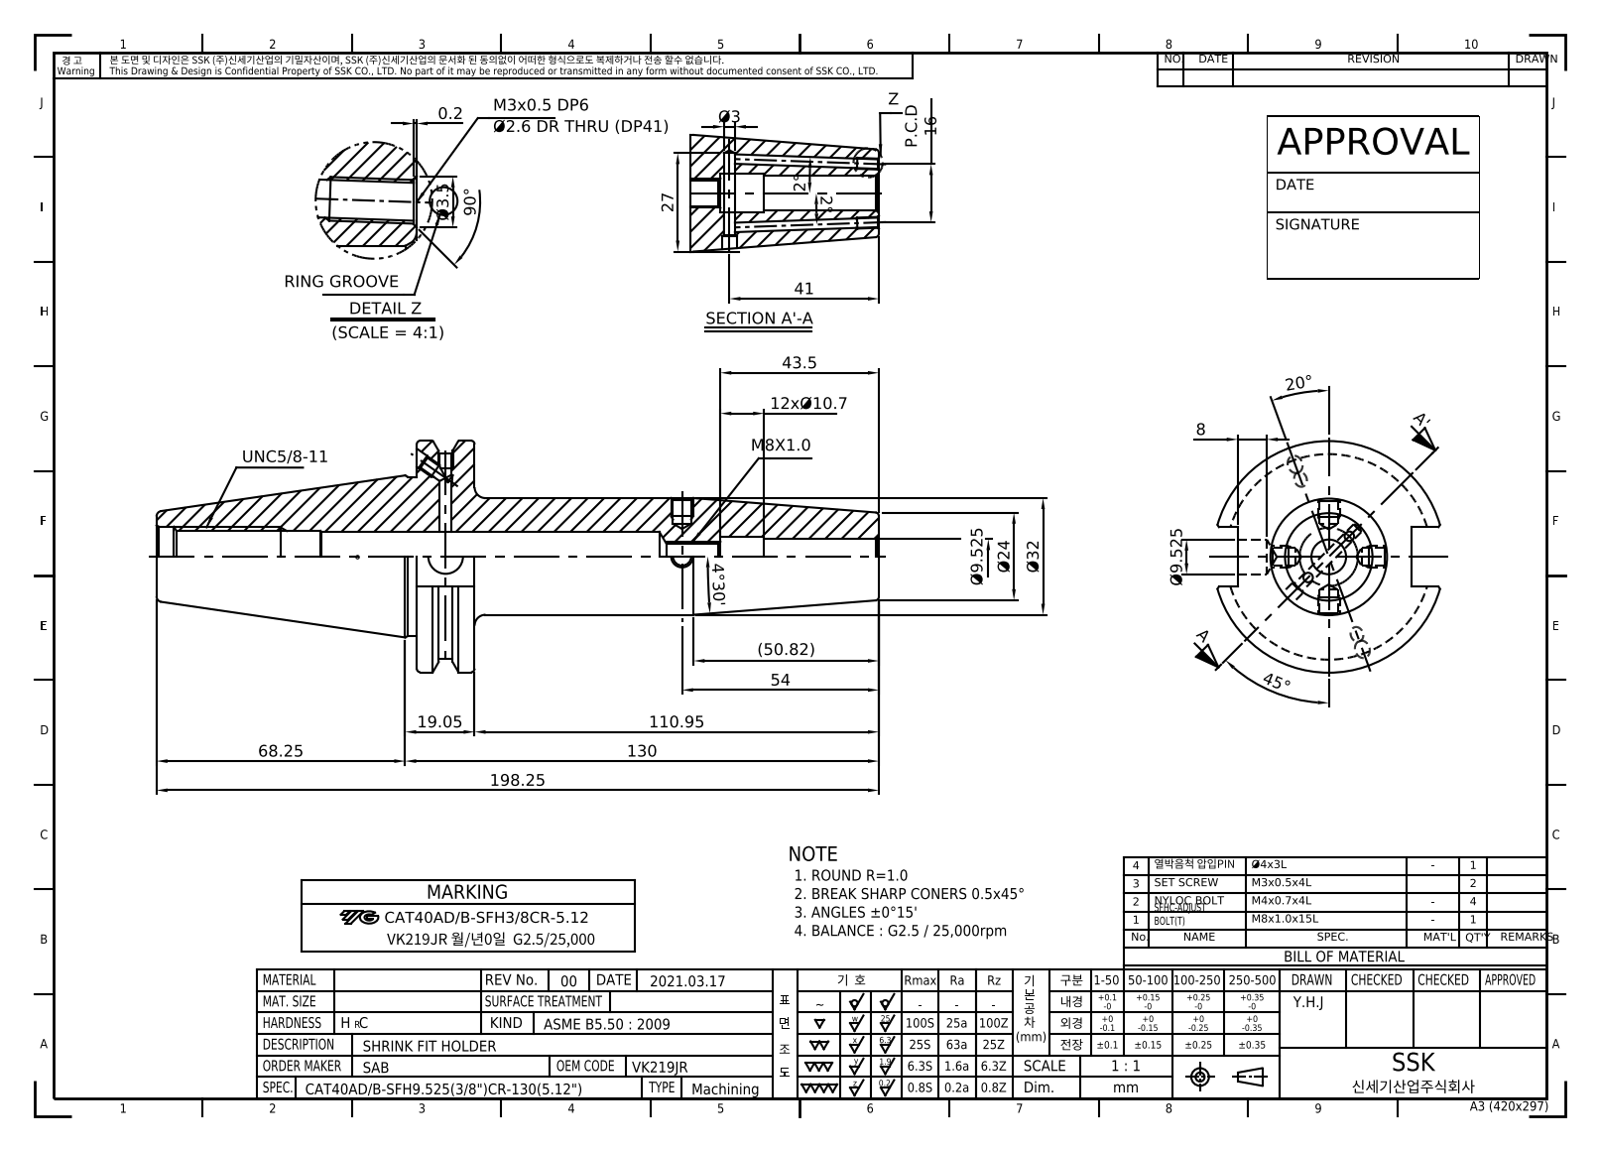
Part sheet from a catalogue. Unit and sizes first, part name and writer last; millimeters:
Units: millimetres
Overall size (bounding box): 198.25 × 63.5 × 61.09
Round holes (diameter × count): ⌀3.24 ×4, ⌀2.46 ×2, ⌀4 ×2, ⌀4.2 ×2, ⌀9.53 ×2, ⌀6.92 ×1, ⌀10.7 ×1, ⌀13 ×1, ⌀13.39 ×1, ⌀16.3 ×1
Round bosses / shafts (diameter × count): ⌀63.5 ×1, ⌀43.6 ×1, ⌀32 ×1
Partial cylindrical surfaces — rounded edges, fillets, slot ends (radius × count): R28.15 ×1
Main face-to-face distances: 15.88, 126.83, 110.95, 47.6, 16.38, 71.42, 87.3, 198.25, 77.47, 6.05
Volume: 169 672 mm³ · Surface area: 35 283 mm²
Bodies: 1 solid, 91 faces (37 planar, 31 cylindrical, 23 other)
Part name (STEP PRODUCT): LO-CAT40ADB-SFH9.525CR-130
STEP written by: Autodesk Inventor 2022 (AUTOMOTIVE_DESIGN)
